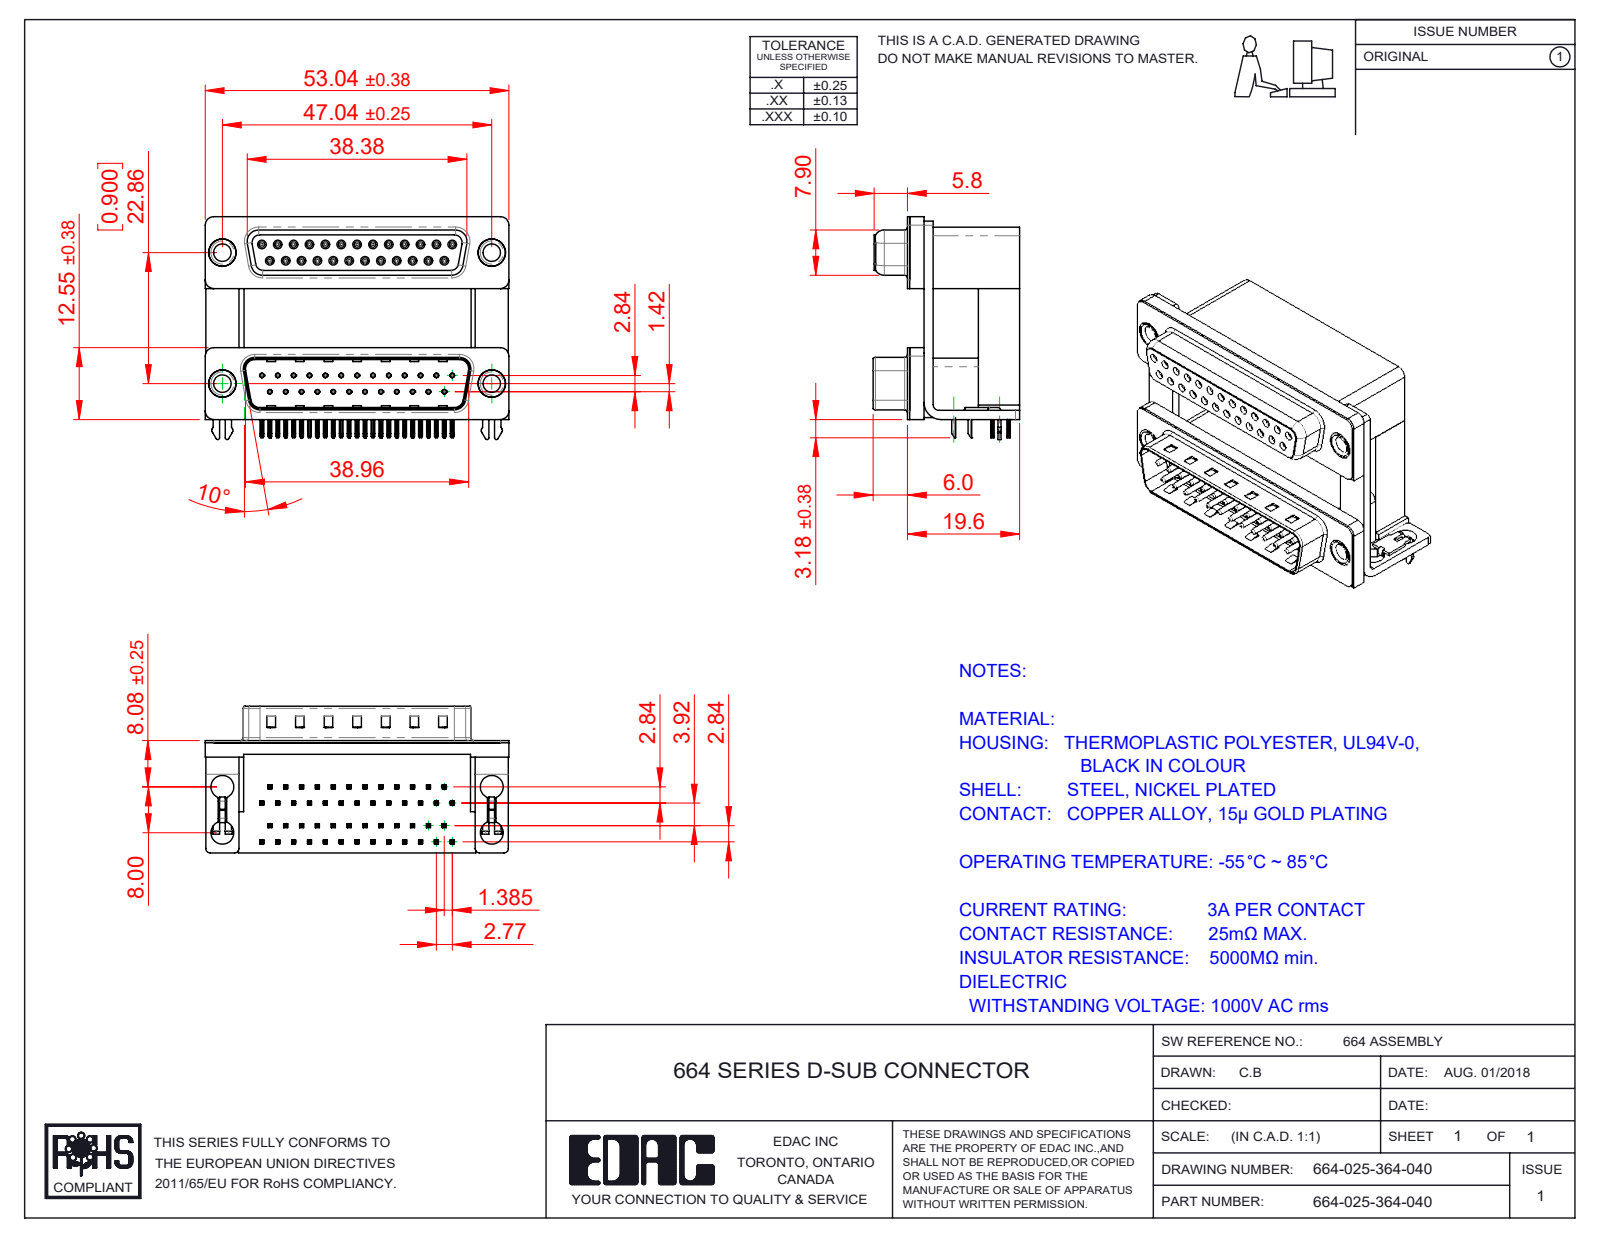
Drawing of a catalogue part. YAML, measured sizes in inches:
part_name: "664 Contact Bottom Lower; 664 Contact Top Lower; 664 Shell Receptacle_25 Contacts; 664-025-364-040 (+8 more)"
step_written_by: "SolidWorks 2020 (CONFIG_CONTROL_DESIGN)"
units: inches
bodies: {solids: 63, faces: 6227, planar: 3335, cylindrical: 1537, other: 1355}
overall_size: [2.088, 1.532, 1.008]
volume: 1.44
surface_area: 39.08
round_holes:
  - {diameter: 0.031, count: 50}
  - {diameter: 0.014, count: 25}
  - {diameter: 0.035, count: 25}
  - {diameter: 0.157, count: 8}
  - {diameter: 0.12, count: 4}
  - {diameter: 0.138, count: 4}
  - {diameter: 0.189, count: 4}
  - {diameter: 0.197, count: 4}
round_bosses_or_shafts:
  - {diameter: 0.047, count: 25}
  - {diameter: 0.03, count: 25}
  - {diameter: 0.193, count: 4}
  - {diameter: 0.187, count: 4}
  - {diameter: 0.152, count: 4}
partial_cylinders:
  - {radius: 0.004, count: 201}
  - {radius: 0.01, count: 106}
  - {radius: 0.006, count: 100}
  - {radius: 0.005, count: 50}
  - {radius: 0.014, count: 50}
  - {radius: 0.013, count: 25}
  - {radius: 0.02, count: 16}
  - {radius: 0.059, count: 14}
face_to_face_distances: [0.756, 0.472, 0.016, 0.283, 0.421, 0.112, 0.657, 0.374, 0.098, 0.488]
hole_center_spacings: [0.109, 0.124, 0.218, 0.327, 0.436, 0.545, 0.654, 0.198]
